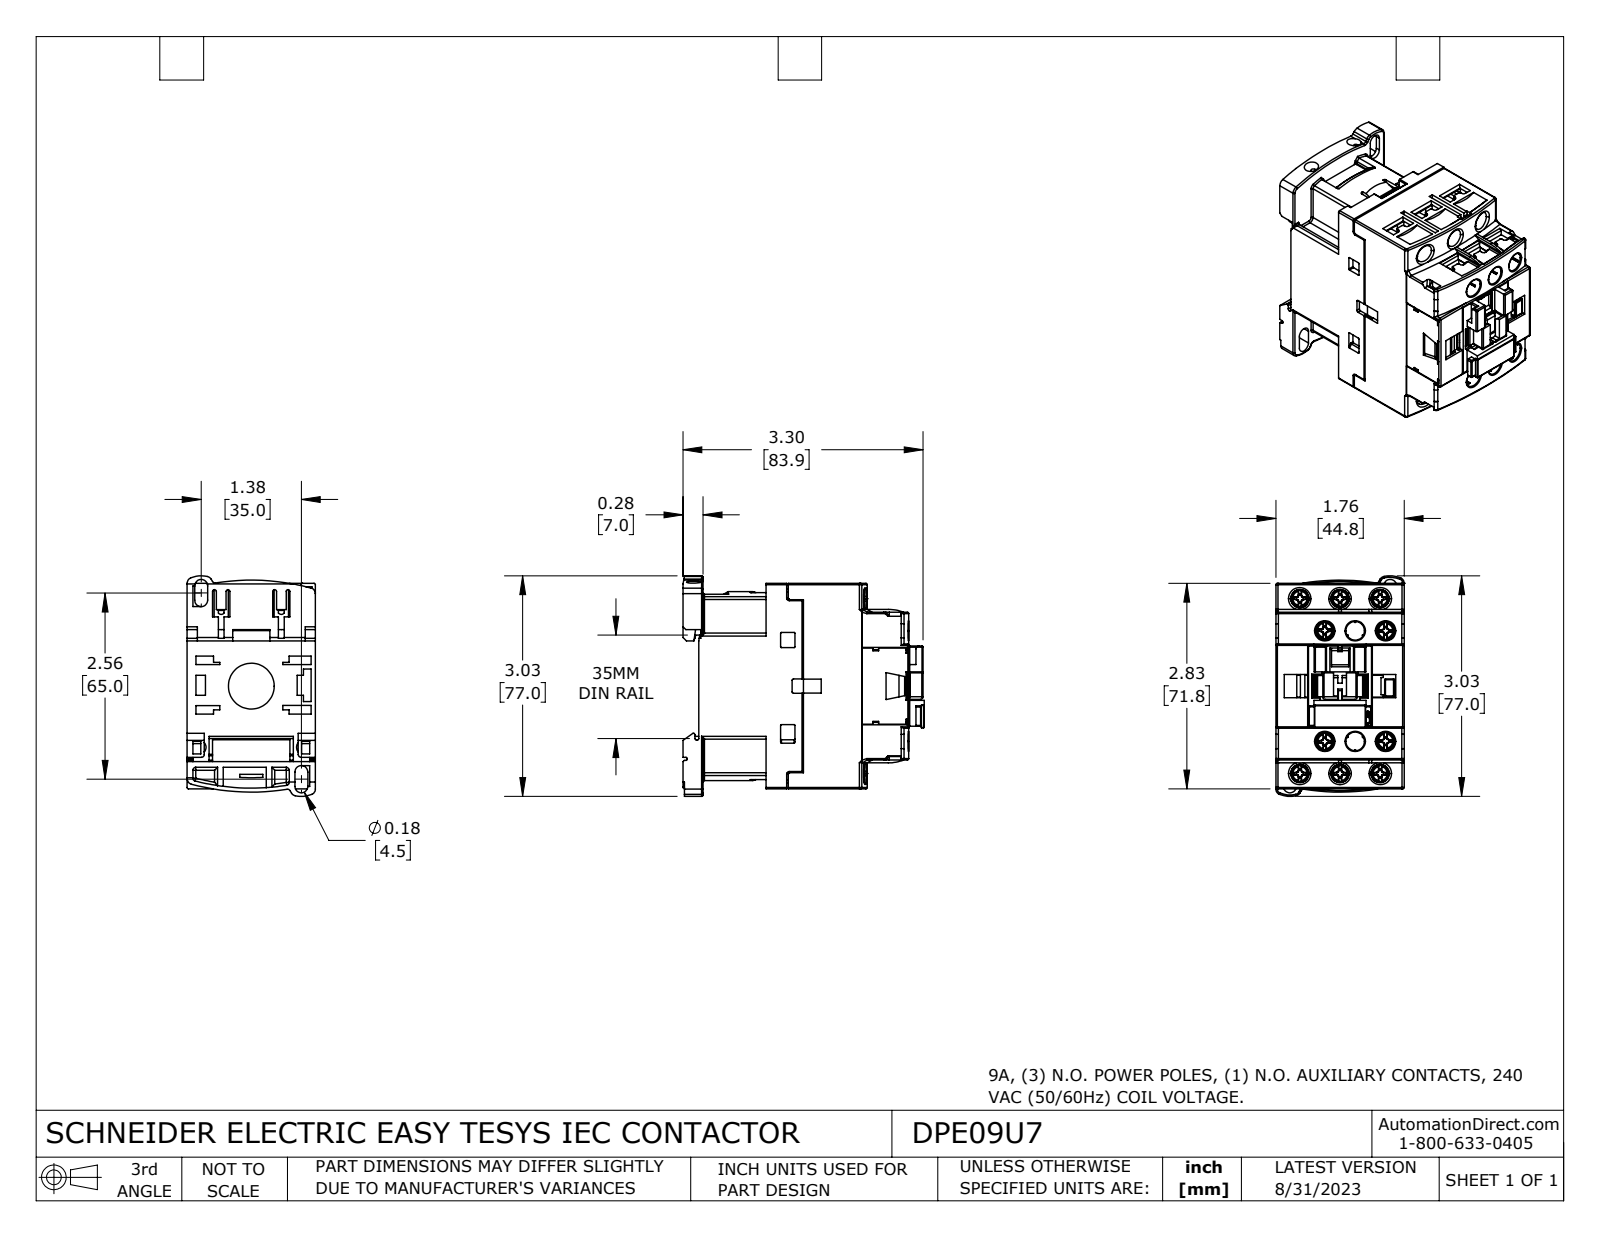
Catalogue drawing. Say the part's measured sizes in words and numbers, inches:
The part is named "DPE09U7". Its 3-D file was written by "SolidWorks 2021 (CONFIG_CONTROL_DESIGN)". It is 20 solids with 3363 faces: 2297 planar, 694 cylindrical and 372 other. Overall it measures 3.317 by 3.031 by 1.783 inches. Its volume is 8.907 cubic inches and its surface area 103.4 square inches. Round holes: 6 of diameter 0.252, 6 of diameter 0.256, 2 of diameter 0.197, 1 of diameter 0.167, 1 of diameter 0.63. Round bosses or shafts: 10 of diameter 0.138, 10 of diameter 0.108, 6 of diameter 0.315. Partial cylindrical surfaces (rounded edges, fillets, slot ends): 78 of radius 0.02, 64 of radius 0.012, 61 of radius 0.039, 42 of radius 0.006, 24 of radius 0.016, 9 of radius 0.63, 8 of radius 0.024, 7 of radius 0.079. The main face-to-face distances are 0.047, 1.764, 1.717, 0.321, 1.128, 0.807, 0.35, 2.78, 1.366, 1.118. The hole center spacings are 0.417, 0.488, 0.551, 0.558, 0.788, 0.878, 1.321, 1.576.
